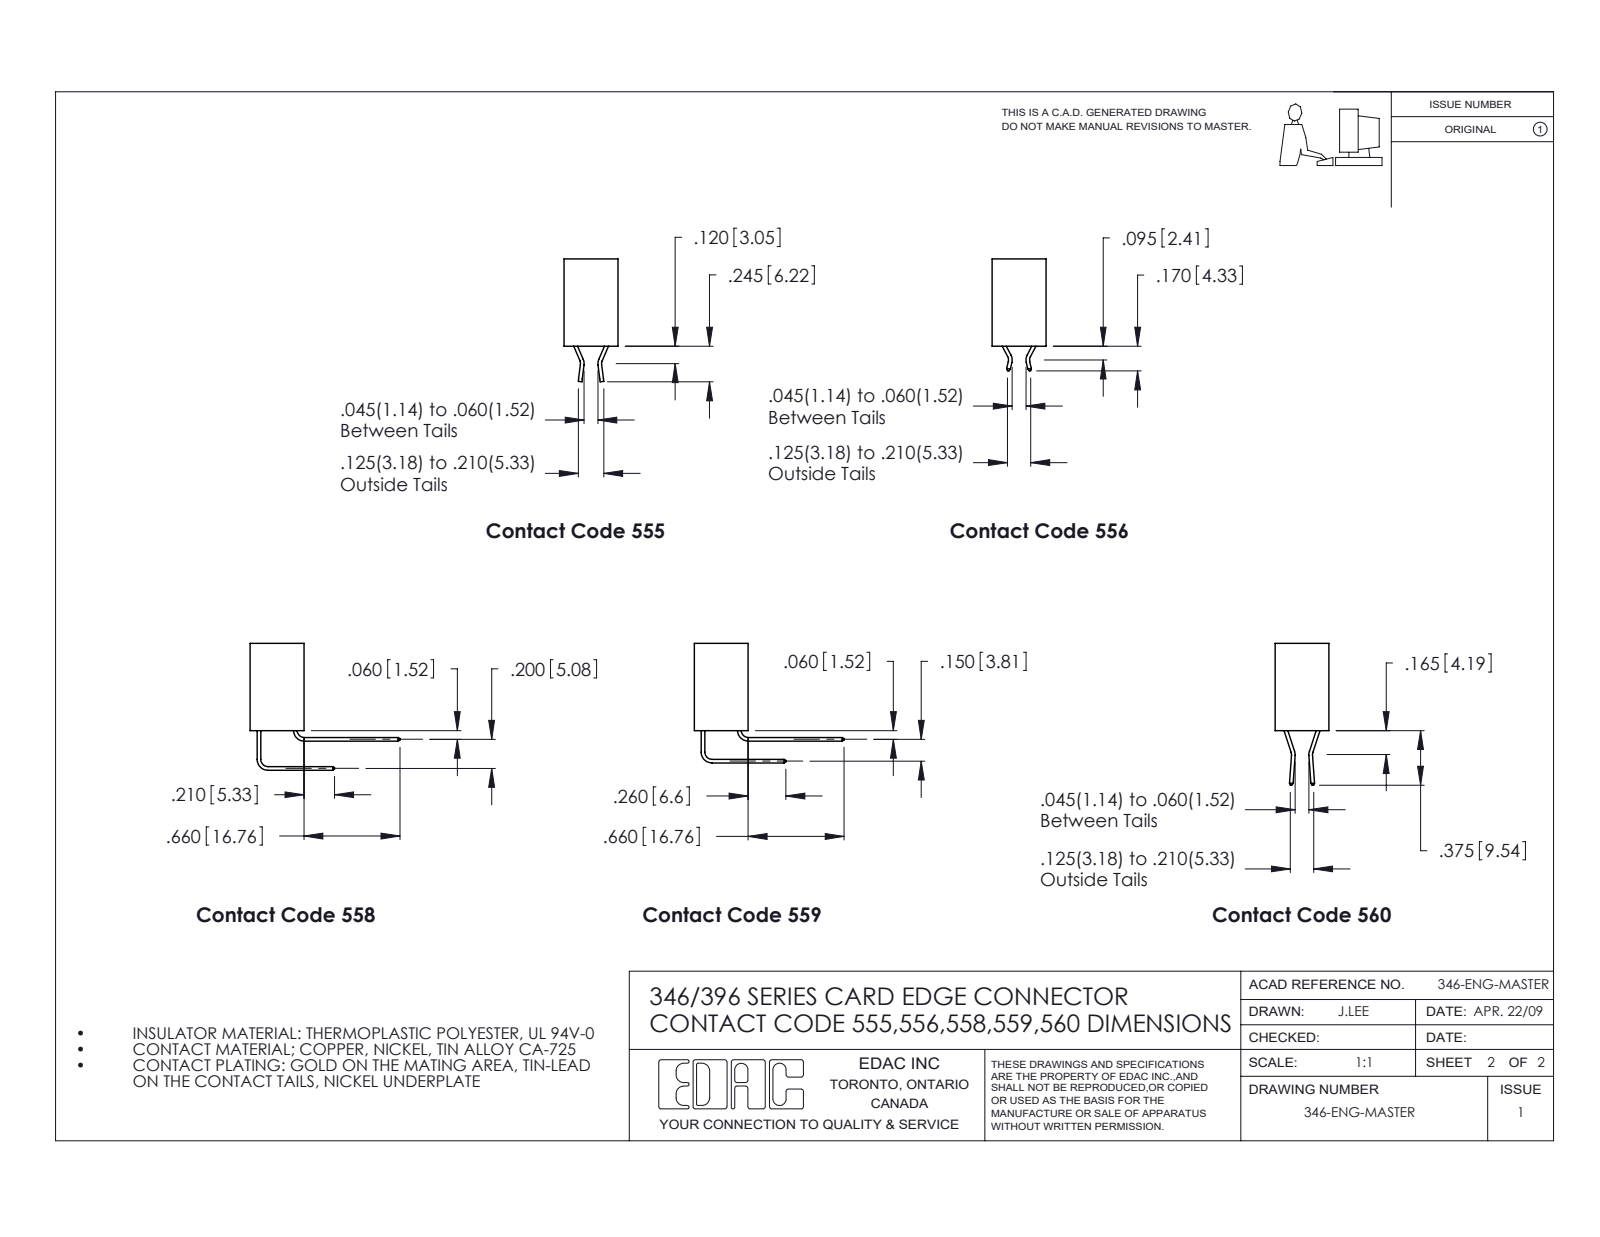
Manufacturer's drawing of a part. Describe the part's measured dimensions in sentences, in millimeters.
The part is named "346-030-556-201; 346 Part_No Mounting Lugs; 345-292-001_556 Tail". Its 3-D file was written by "SolidWorks 2020 (CONFIG_CONTROL_DESIGN)". It is 31 solids with 1854 faces: 1242 planar, 612 cylindrical and 0 other. Overall it measures 54.9 by 19.6 by 9.4 millimeters. Its volume is 5 720 cubic millimeters and its surface area 7 561 square millimeters. Round holes: 1 of diameter 1.6. Partial cylindrical surfaces (rounded edges, fillets, slot ends): 45 of radius 0.2, 22 of radius 0.3, 6 of radius 0.2, 6 of radius 0.8, 3 of radius 0.7, 2 of radius 0.3, 2 of radius 0.4, 2 of radius 0.6. The main face-to-face distances are 1.2, 8.2, 6.4, 9.4, 0.6, 1.8, 7.6, 7, 3.8, 5.6.
